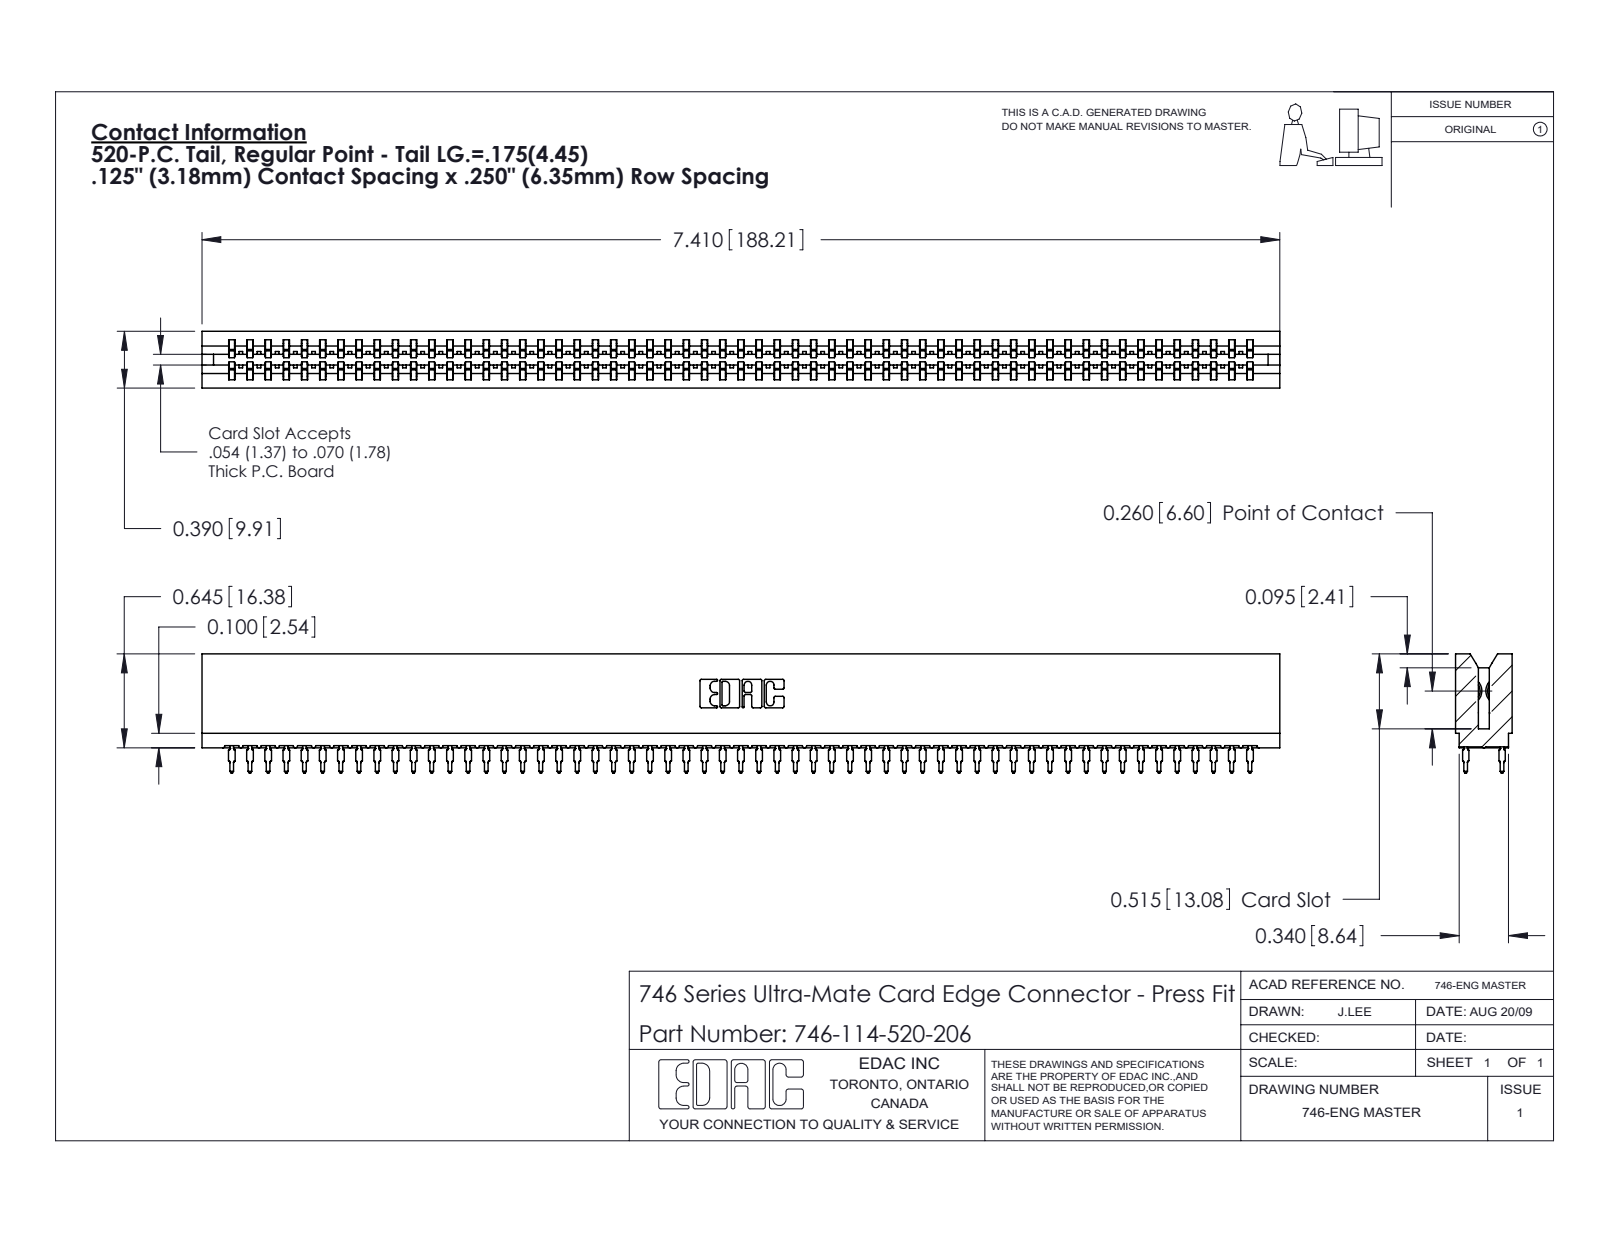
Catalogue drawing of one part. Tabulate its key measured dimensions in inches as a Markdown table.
| quantity | value |
| --- | --- |
| part name | 746-114-520-206; 746-292-001_520; 746 Part_.515 Slot Depth - 06 |
| STEP written by | SolidWorks 2020 (CONFIG_CONTROL_DESIGN) |
| units | inches |
| bodies | 115 solids, 10301 faces (5300 planar, 2037 cylindrical, 2964 other) |
| overall size | 7.41 × 0.819 × 0.39 |
| volume | 1.218 in³ |
| surface area | 49.36 in² |
| partial cylindrical surfaces (radius × count) | 0.021 × 228, 0.015 × 58, 0.01 × 22, 0.005 × 8, 0.011 × 8, 0.007 × 6, 0.031 × 6, 0.026 × 3 |
| main face-to-face distances | 0.057, 0.333, 0.39, 0.25, 0.025, 0.307, 0.275, 0.083, 0.174, 0.158 |
